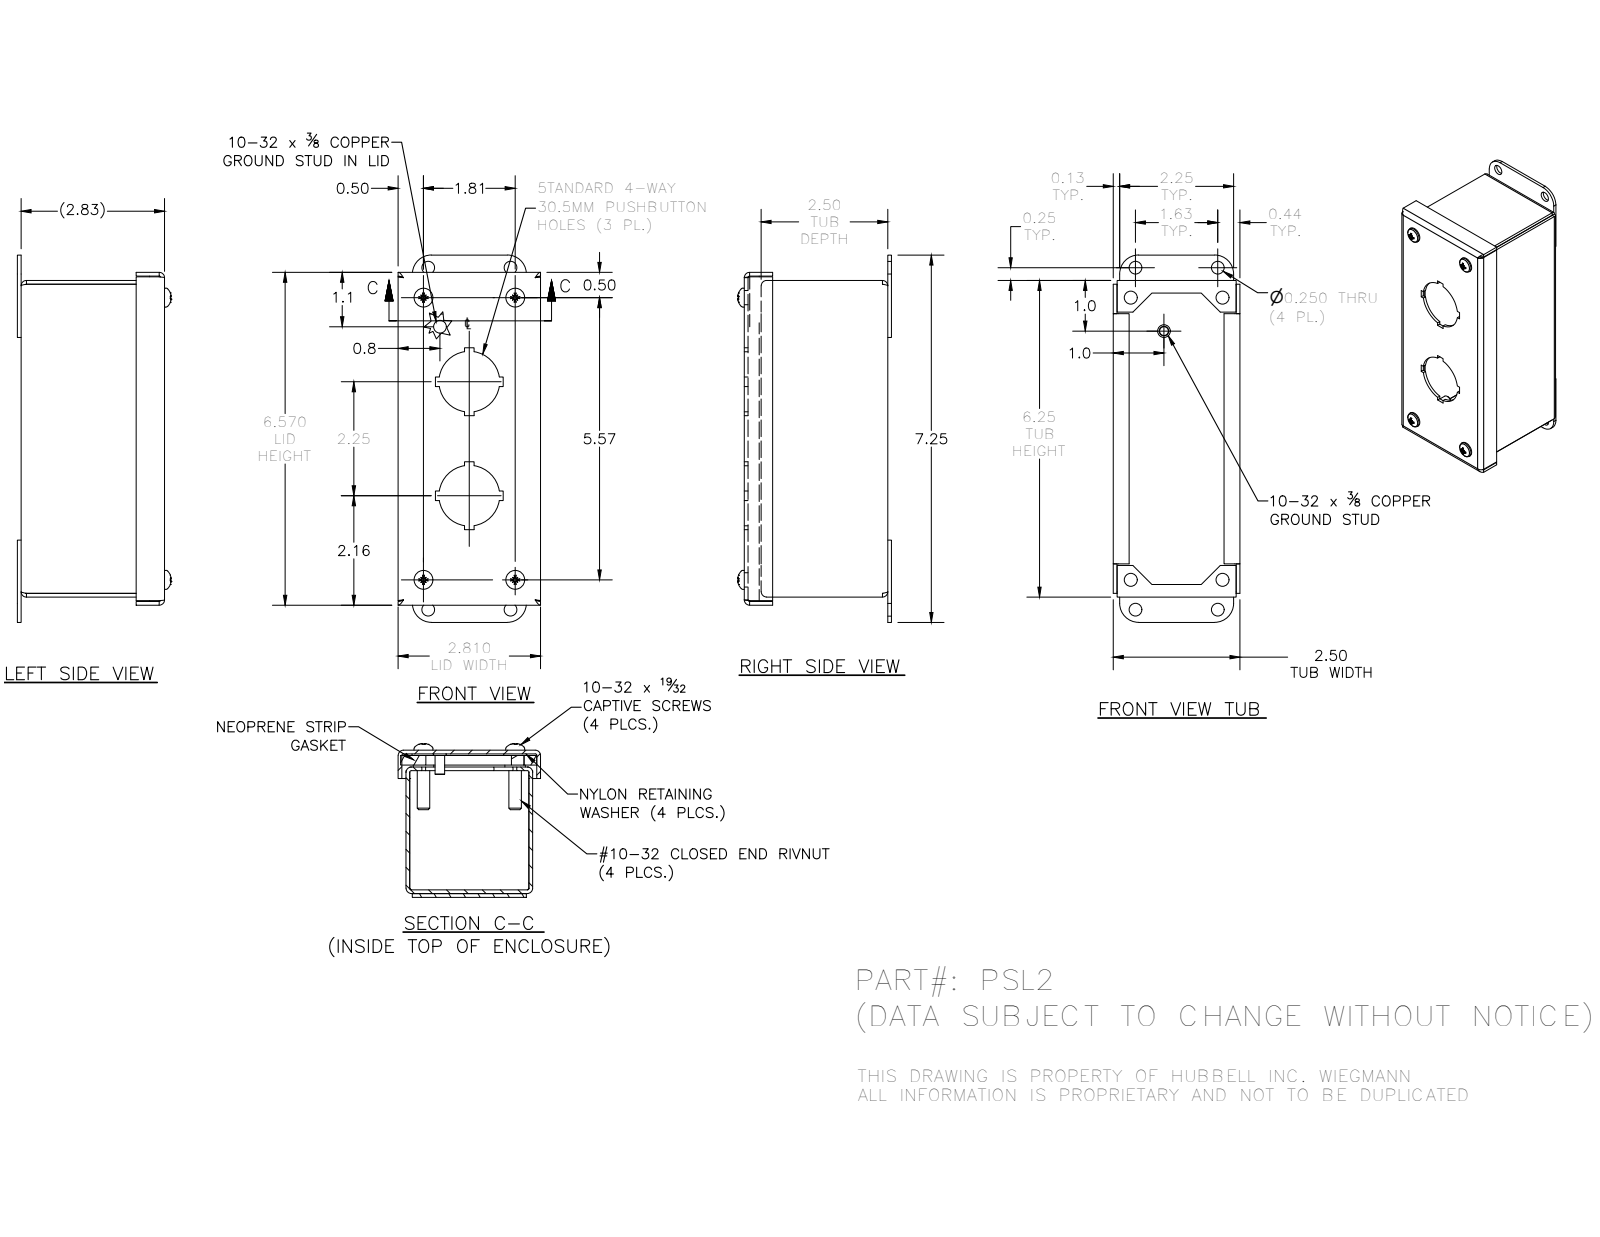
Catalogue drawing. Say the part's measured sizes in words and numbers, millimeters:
The part is named "PSL2LID; 372163; 39077; PSL2BKP (+5 more)". Its 3-D file was written by "Autodesk Inventor 2016 (AUTOMOTIVE_DESIGN)". It is 20 solids with 520 faces: 302 planar, 104 cylindrical and 114 other. Overall it measures 184.15 by 77.11 by 71.37 millimeters. Its volume is 140 900 cubic millimeters and its surface area 143 659 square millimeters. Round holes: 4 of diameter 3.96, 4 of diameter 4.98, 4 of diameter 6.35, 4 of diameter 6.53, 4 of diameter 7.06, 4 of diameter 7.14, 4 of diameter 7.95, 2 of diameter 30.48. Round bosses or shafts: 6 of diameter 4.83, 4 of diameter 11.51, 4 of diameter 10.31, 4 of diameter 9.47, 4 of diameter 6.3, 2 of diameter 6.35. Partial cylindrical surfaces (rounded edges, fillets, slot ends): 12 of radius 0.79, 12 of radius 2.67, 4 of radius 2.27, 4 of radius 9.53. The main face-to-face distances are 1.88, 61.62, 70.05, 71.93, 63.5, 59.74, 68.17, 156.87, 4.78, 7.47. The hole center spacings are 116.15, 48.02, 101.94, 15.16, 15.17, 45.97, 46.12, 47.63.
